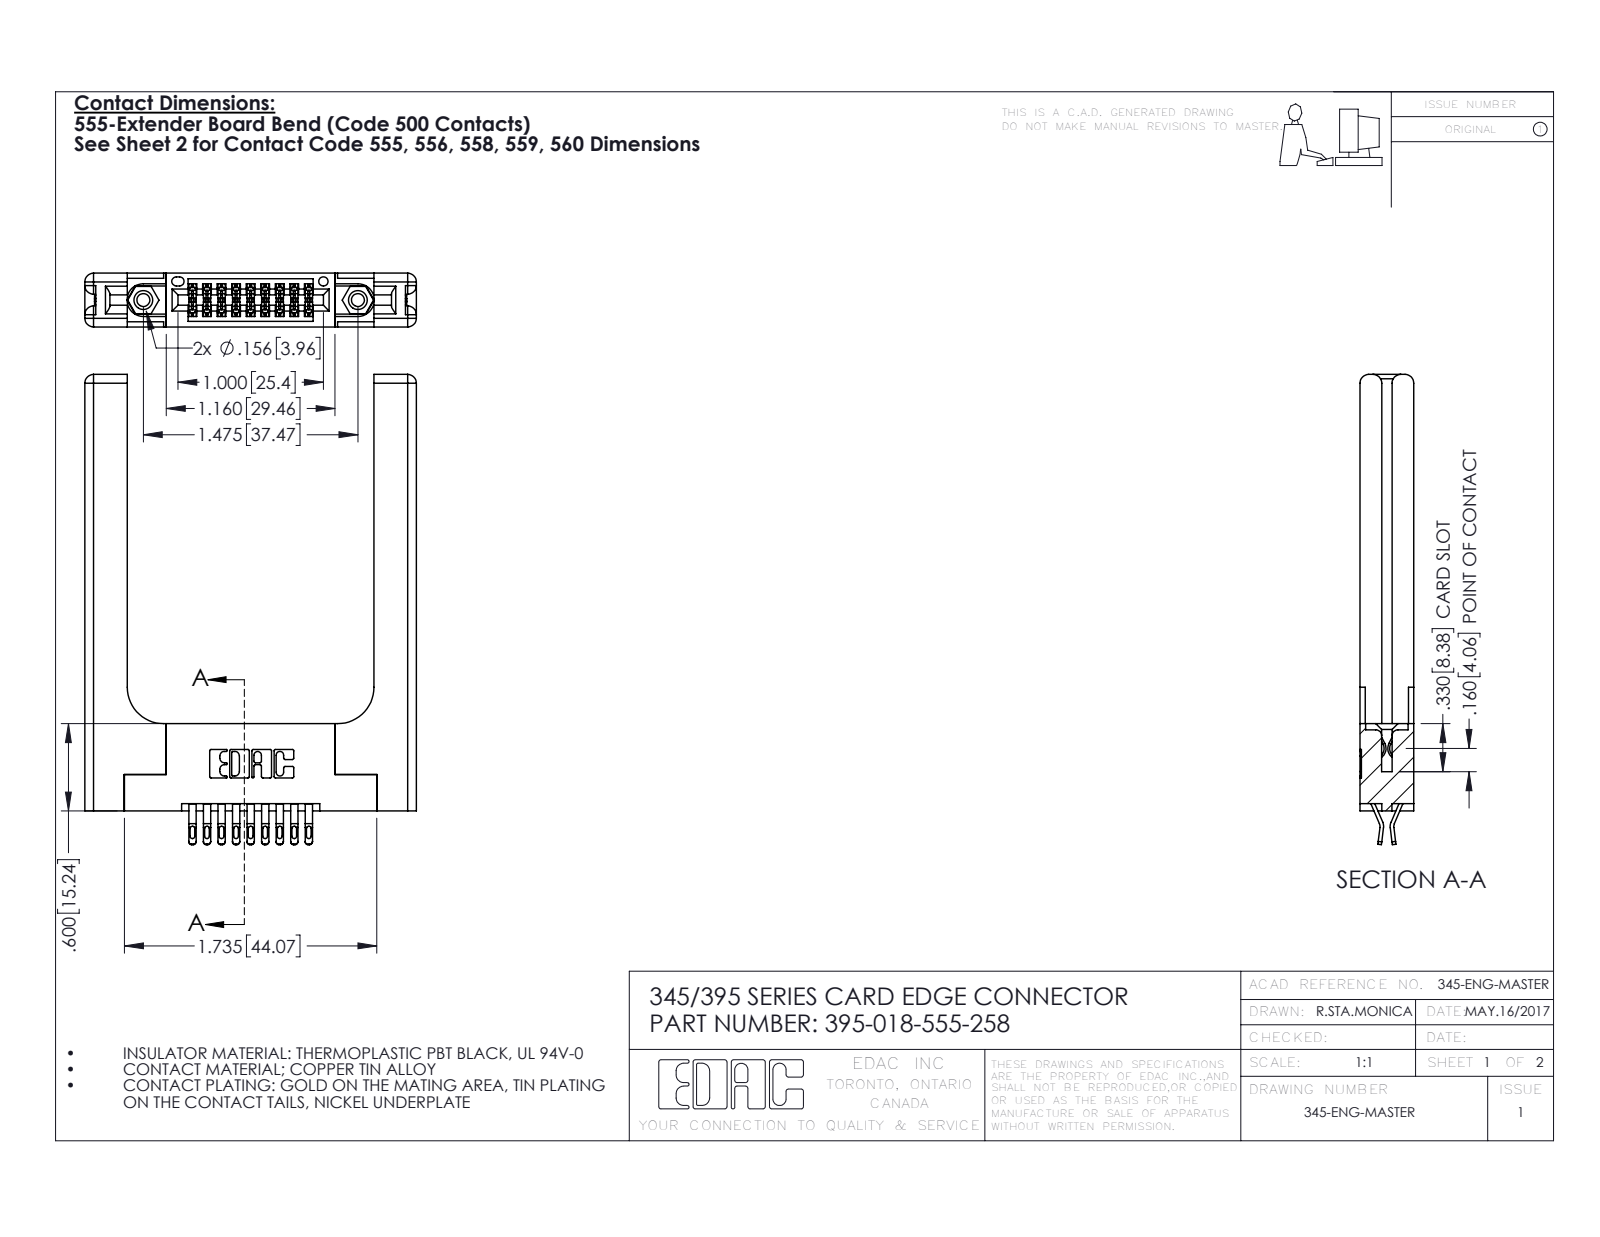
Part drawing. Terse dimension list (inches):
name: 395-018-555-258; 345-220-058_345-220-058; 345 Part_Flush Mounting Lugs - 0.156 Dia-TH; 345-292-001_555 Tail (+1 more)
written by: SolidWorks 2016 (CONFIG_CONTROL_DESIGN)
unit: in
bodies: 23 solids, 1390 faces (786 planar, 544 cylindrical, 60 other)
size: 3.232 × 2.279 × 0.37
volume: 0.845 in³; area: 19.43 in²
holes: 2× ⌀0.089, 2× ⌀0.125, 2× ⌀0.156, 1× ⌀0.064
bosses: 2× ⌀0.155
rounds: 45× R0.016, 36× R0.02, 27× R0.006, 22× R0.01, 16× R0.06, 6× R0.007, 6× R0.031, 3× R0.026
face distances: 0.37, 0.15, 0.072, 0.22, 0.077, 0.148, 0.298, 0.2, 1.696, 0.071
hole spacings: 0.27, 1.244, 1.475
